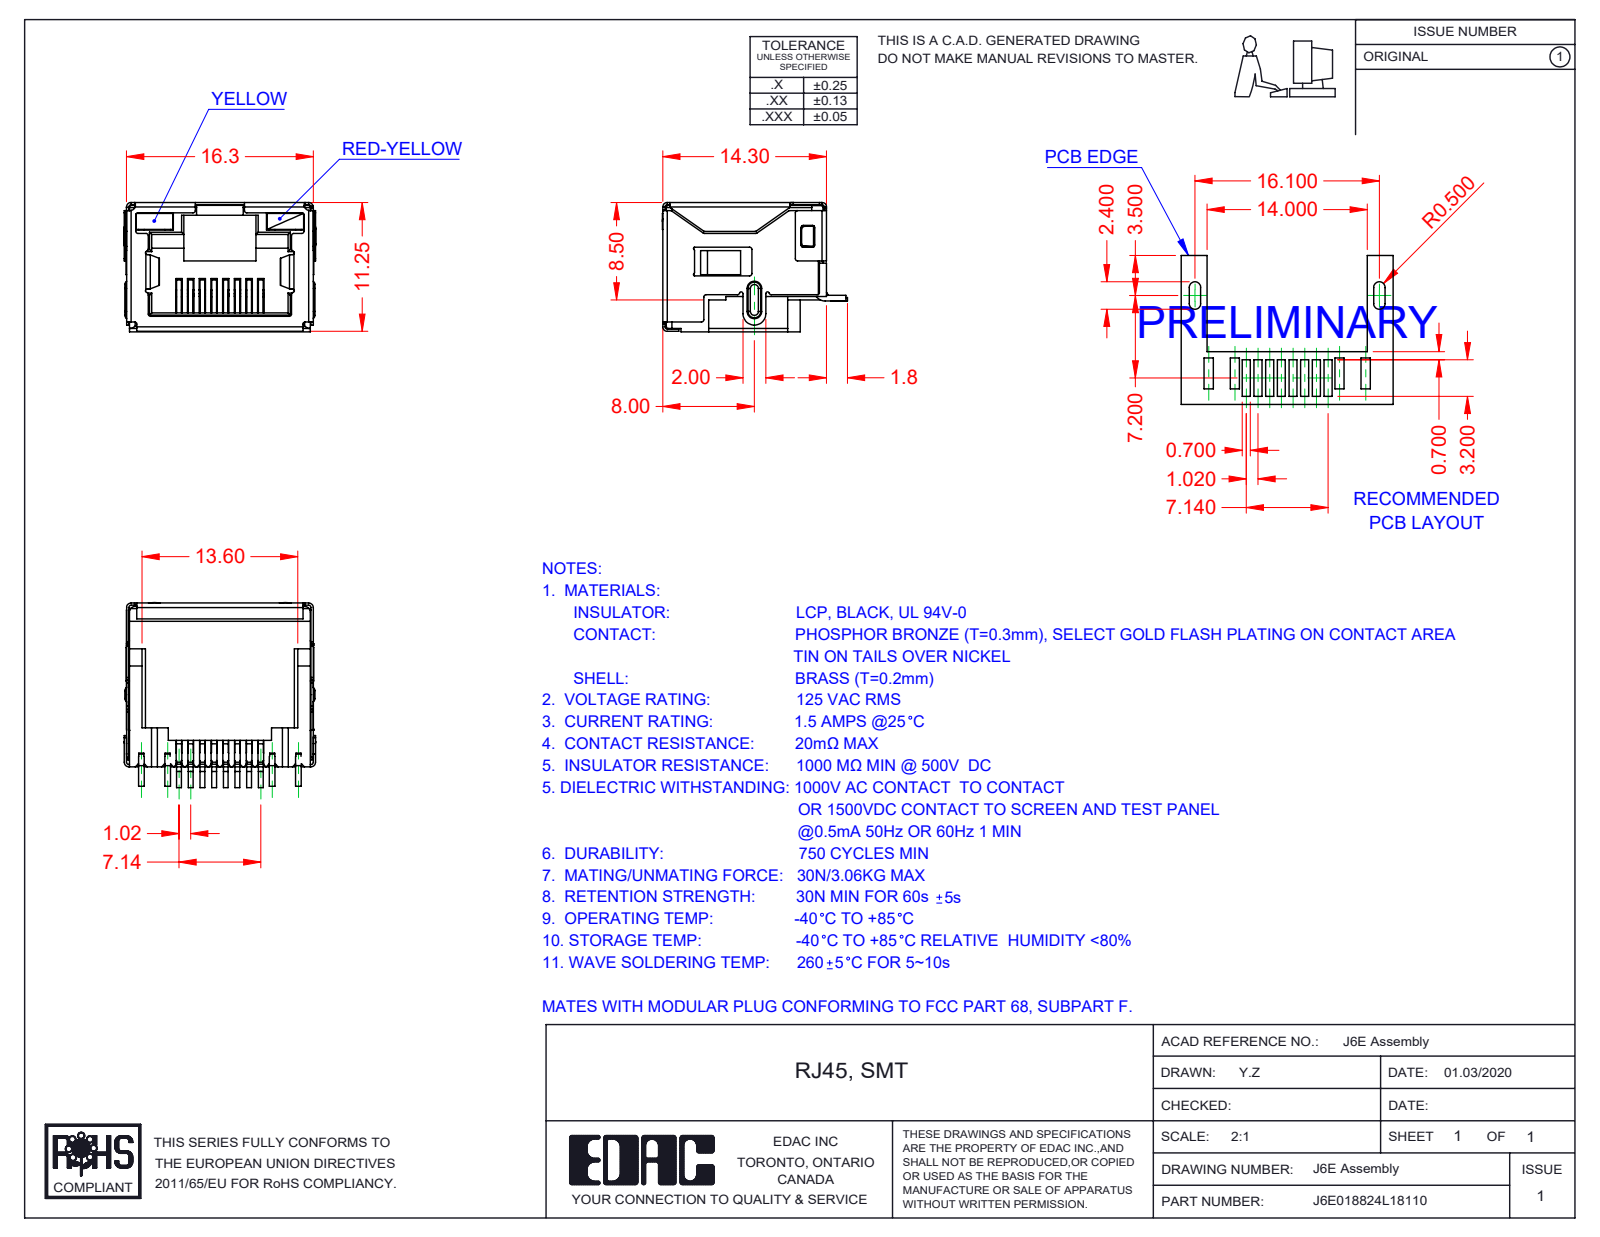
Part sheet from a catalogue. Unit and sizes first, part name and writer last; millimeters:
Units: millimetres
Overall size (bounding box): 16.75 × 16.15 × 11.3
Partial cylindrical surfaces — rounded edges, fillets, slot ends (radius × count): R0.2 ×82, R0.25 ×17, R0.4 ×13, R0.5 ×13, R0.1 ×10, R0.15 ×7, R0.3 ×4, R1 ×3
Main face-to-face distances: 11.05, 16.05, 16.1, 15.85, 11.1, 11.3, 2.4, 0.7, 9.85, 0.49
Volume: 1 109 mm³ · Surface area: 4 045 mm²
Bodies: 12 solids, 1498 faces (1099 planar, 349 cylindrical, 50 other)
Part name (STEP PRODUCT): J6E018824L18110; 6E Contacts; 6E LED RH_8-Red-Yellow; 6E LED LH_1-Yellow (+2 more)
STEP written by: SolidWorks 2016 (CONFIG_CONTROL_DESIGN)
